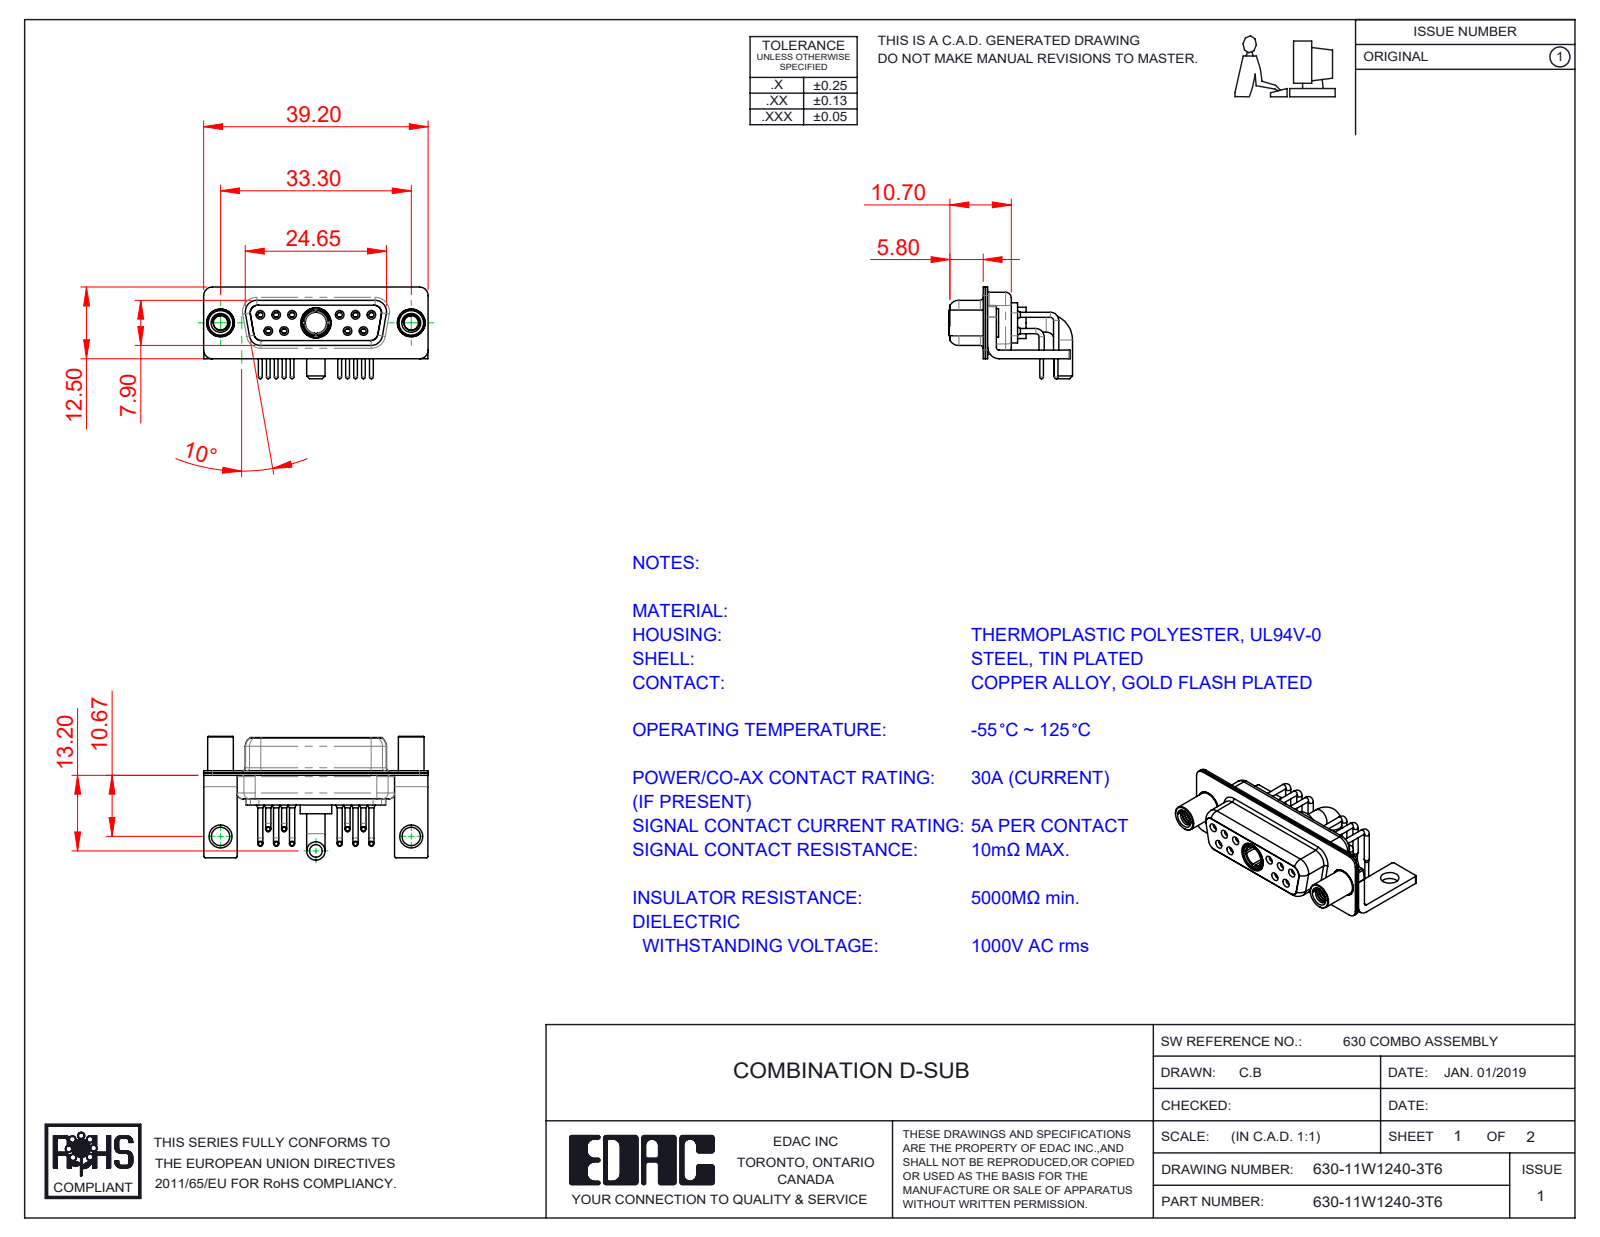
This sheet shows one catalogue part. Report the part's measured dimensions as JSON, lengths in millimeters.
{"part_name": "630Combo Shell Rear_15 Contacts; 630Combo Contact Row 1; 630Combo Housing_11W1; 630Combo Shell Front_15 Contacts (+5 more)", "step_written_by": "SolidWorks 2020 (CONFIG_CONTROL_DESIGN)", "units": "millimeters", "bodies": {"solids": 19, "faces": 985, "planar": 268, "cylindrical": 464, "other": 253}, "overall_size": [39.2, 21.6, 16], "volume_mm3": 3058, "surface_area_mm2": 7215, "round_holes": [[0.9, 10], [1.1, 10], [1.5, 10], [2, 10], [1.7, 6], [1.6, 4], [4.85, 3], [2.5, 2], [3.2, 2], [4, 2], [4.05, 2], [3.7, 1]], "round_bosses_or_shafts": [[0.9, 10], [0.65, 10], [1.6, 6], [5, 2], [4.95, 2], [4.8, 2], [4.5, 2], [3.2, 2]], "partial_cylinders_radius": [[0.25, 16], [1.5, 16], [2, 13], [1.35, 12], [1.6, 8], [0.5, 5], [0.6, 4], [0.65, 4]], "face_to_face_distances": [0.4, 0.8, 1.4, 0.45, 8.45, 1.5, 1.8, 8.9, 6.2, 2.3], "hole_center_spacings": [3.16, 2.77, 13.85, 11.08, 16.62, 5.03, 5.04, 5.54]}
